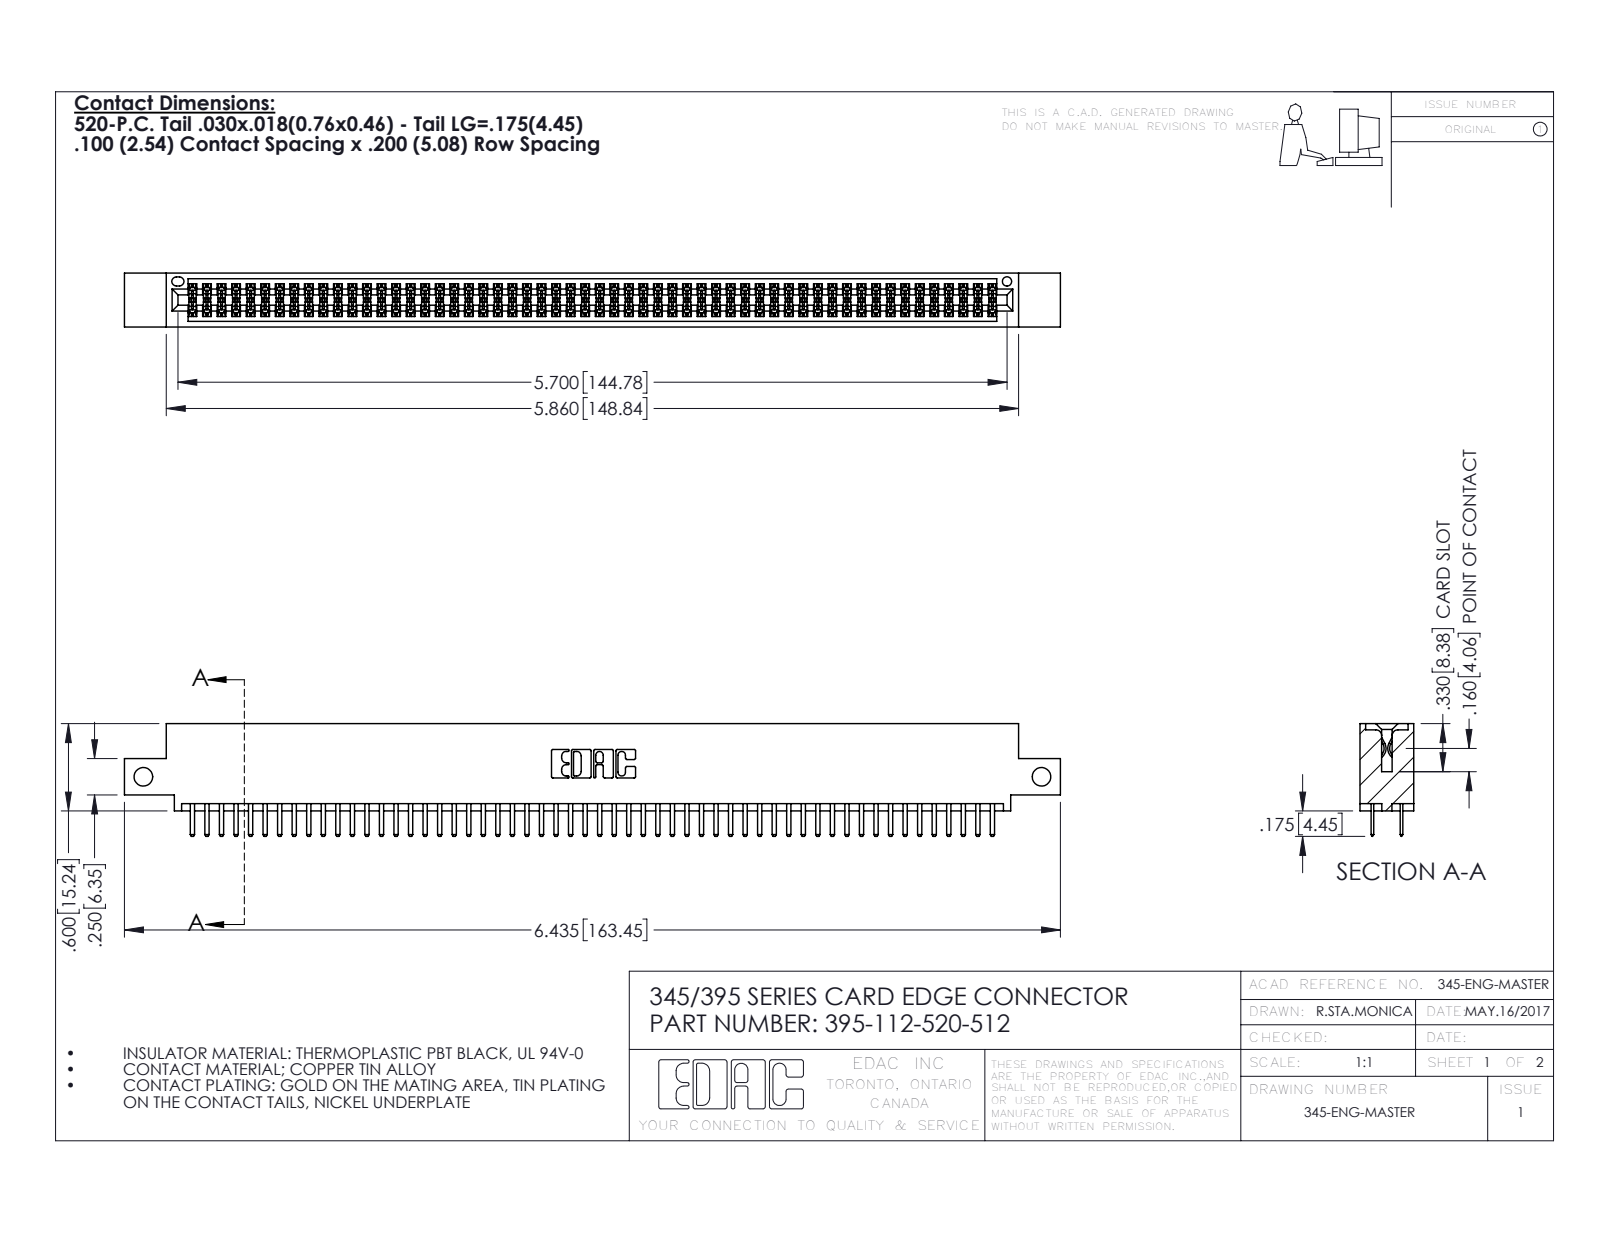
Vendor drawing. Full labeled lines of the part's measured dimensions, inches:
Part name (STEP PRODUCT): 345 Part_0.110 Offset - Side Mount; 345-292-001_345-293-120; 395-112-520-512
STEP written by: SolidWorks 2016 (CONFIG_CONTROL_DESIGN)
Units: inches
Bodies: 113 solids, 6178 faces (4004 planar, 2174 cylindrical, 0 other)
Overall size (bounding box): 6.435 × 0.775 × 0.37
Volume: 0.964 in³ · Surface area: 36.39 in²
Round holes (diameter × count): ⌀0.128 ×2, ⌀0.064 ×1
Partial cylindrical surfaces — rounded edges, fillets, slot ends (radius × count): R0.006 ×168, R0.01 ×116, R0.01 ×22, R0.007 ×6, R0.031 ×6, R0.026 ×3, R0.014 ×2, R0.019 ×2
Main face-to-face distances: 0.298, 0.072, 0.2, 0.37, 0.098, 0.272, 0.025, 0.225, 0.022, 0.072
Hole centre spacings: 6.175
